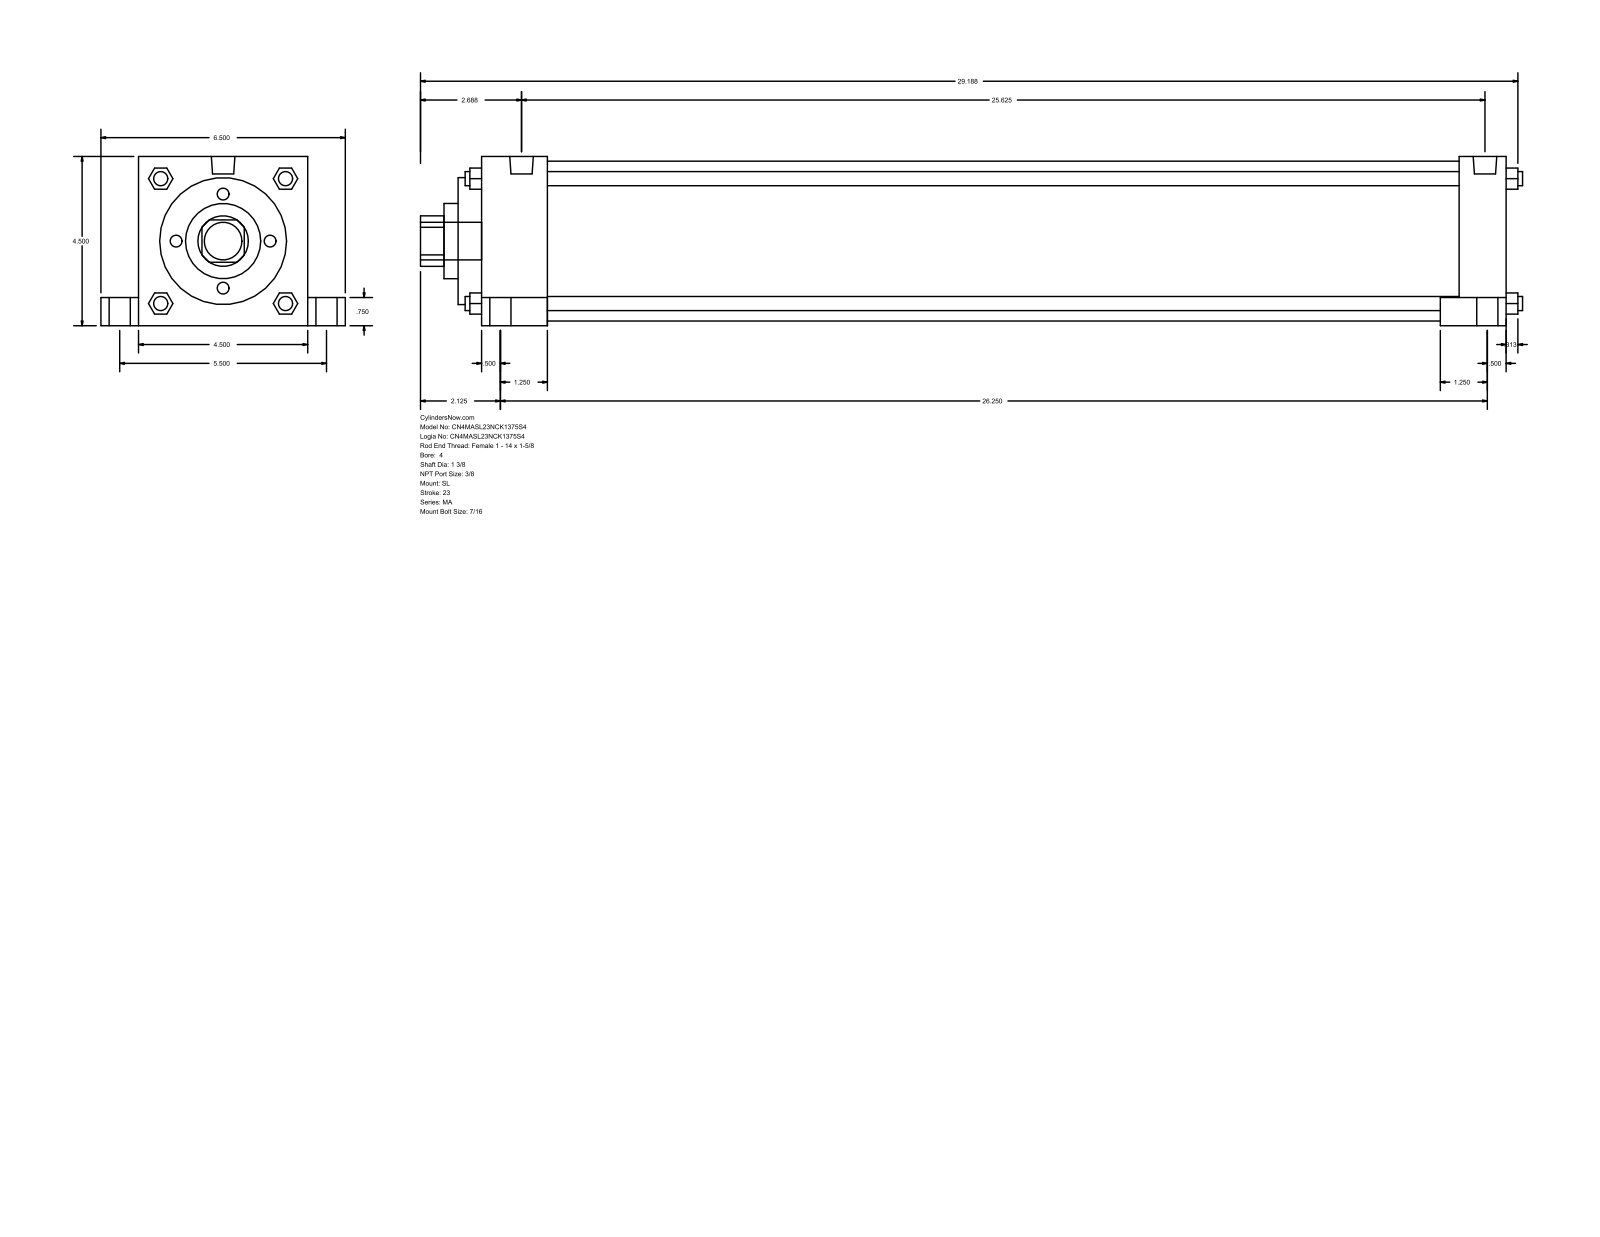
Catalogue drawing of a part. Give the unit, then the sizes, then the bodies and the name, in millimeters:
Units: millimetres
Overall size (bounding box): 744.54 × 165.1 × 114.3
Round holes (diameter × count): ⌀34.92 ×1, ⌀50.8 ×1, ⌀85.72 ×1, ⌀107.95 ×1
Round bosses / shafts (diameter × count): ⌀20.64 ×4, ⌀14.29 ×4, ⌀11.11 ×4, ⌀9.53 ×4, ⌀15.93 ×2, ⌀25.4 ×1
Partial cylindrical surfaces — rounded edges, fillets, slot ends (radius × count): R17.06 ×1
Main face-to-face distances: 114.3, 692.15, 615.95, 708.02, 15.87, 60.32, 44.45, 647.7, 676.27, 660.4
Bodies: 0 solids, 150 faces (113 planar, 37 cylindrical, 0 other)
Part name (STEP PRODUCT): MA_SL__0400_1.375
STEP written by: GSSL Pune (CONFIG_CONTROL_DESIGN)
